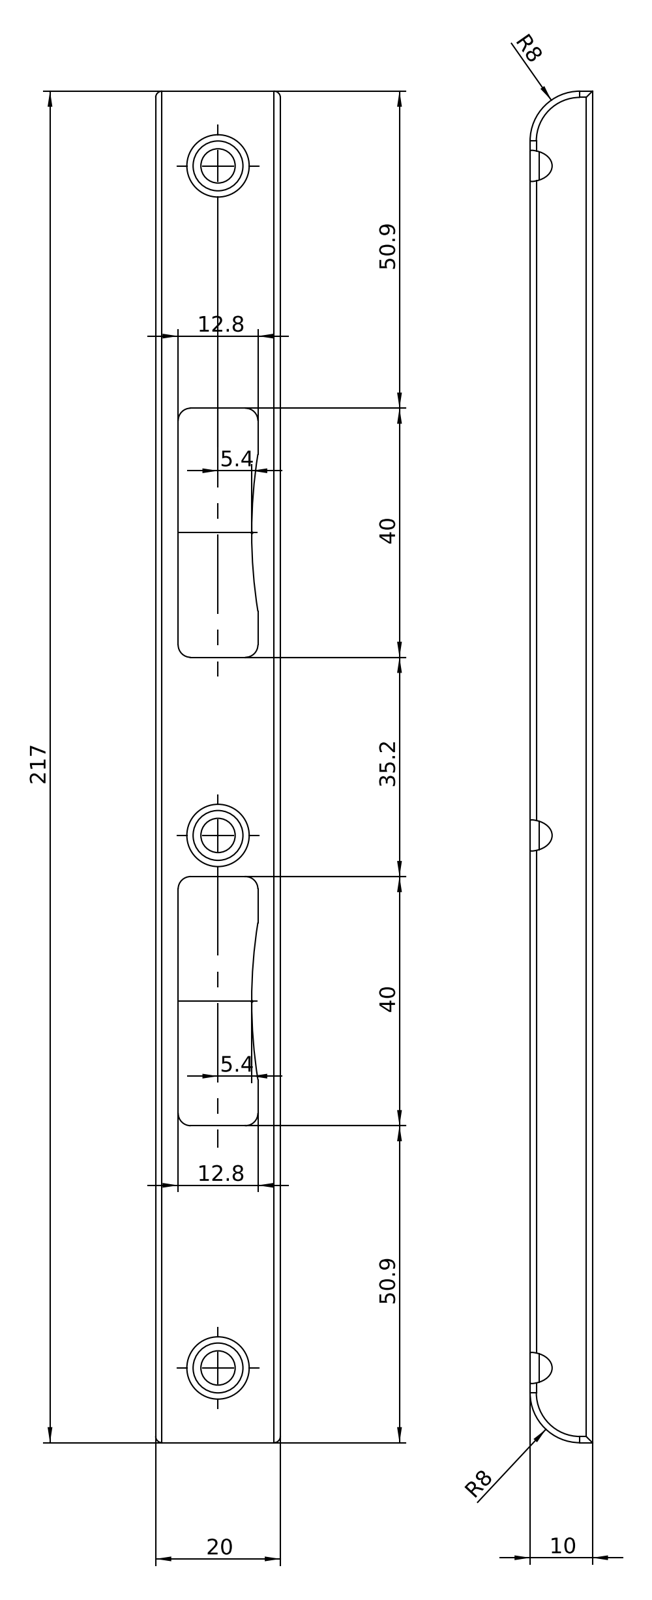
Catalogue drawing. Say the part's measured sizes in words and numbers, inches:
The part is named "B-40341.1542_D001169255-001". Its 3-D file was written by "SolidWorks 2021 (AUTOMOTIVE_DESIGN)". It is 1 solid with 91 faces: 30 planar, 51 cylindrical and 10 other. Overall it measures 8.543 by 0.787 by 0.394 inches. Its volume is 0.831 cubic inches and its surface area 29.71 square inches. Round holes: 3 of diameter 0.197, 3 of diameter 0.217, 3 of diameter 0.315. Partial cylindrical surfaces (rounded edges, fillets, slot ends): 8 of radius 0.039, 8 of radius 0.079, 2 of radius 0.315, 2 of radius 3.15. The main face-to-face distances are 0.059, 0.335, 0.728, 0.394, 0.276, 0.787, 0.669, 0.142, 0.646, 0.083. The hole center spacings are 3.366, 4.232, 7.598.
